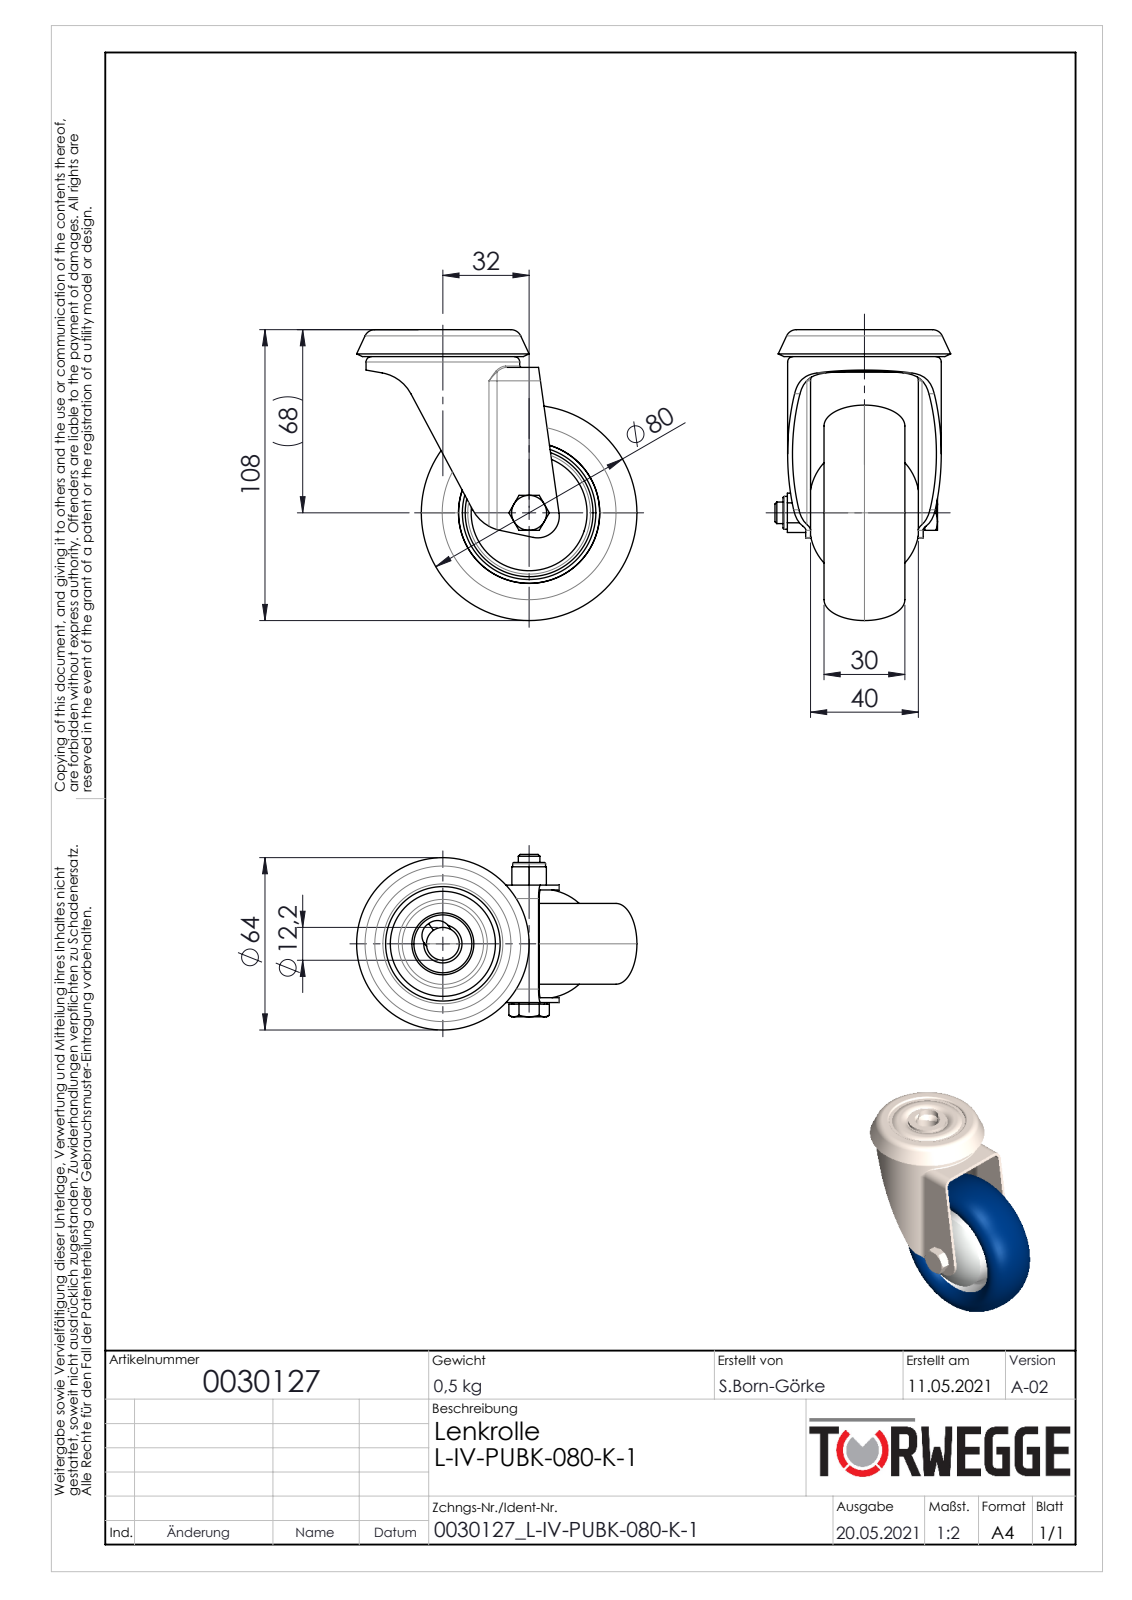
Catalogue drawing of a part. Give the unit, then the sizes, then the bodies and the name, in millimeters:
Units: millimetres
Overall size (bounding box): 108 × 104 × 65.2
Round holes (diameter × count): ⌀6.65 ×1, ⌀8 ×1, ⌀8.3 ×1, ⌀12.2 ×1, ⌀33 ×1, ⌀35 ×1, ⌀53.4 ×1
Round bosses / shafts (diameter × count): ⌀57 ×1, ⌀29 ×1, ⌀21.5 ×1, ⌀15 ×1, ⌀13 ×1, ⌀12.2 ×1
Partial cylindrical surfaces — rounded edges, fillets, slot ends (radius × count): R5 ×4, R3.2 ×2, R5.25 ×2, R6.8 ×2, R15 ×2, R8 ×1
Main face-to-face distances: 1.8, 41.8, 8.5, 10.05, 33.55, 8.25, 31.75, 40, 43.6, 10.3
Volume: 157 016 mm³ · Surface area: 69 354 mm²
Bodies: 7 solids, 225 faces (59 planar, 54 cylindrical, 112 other)
Part name (STEP PRODUCT): 0030127
STEP written by: SolidWorks 2020 (AUTOMOTIVE_DESIGN)
